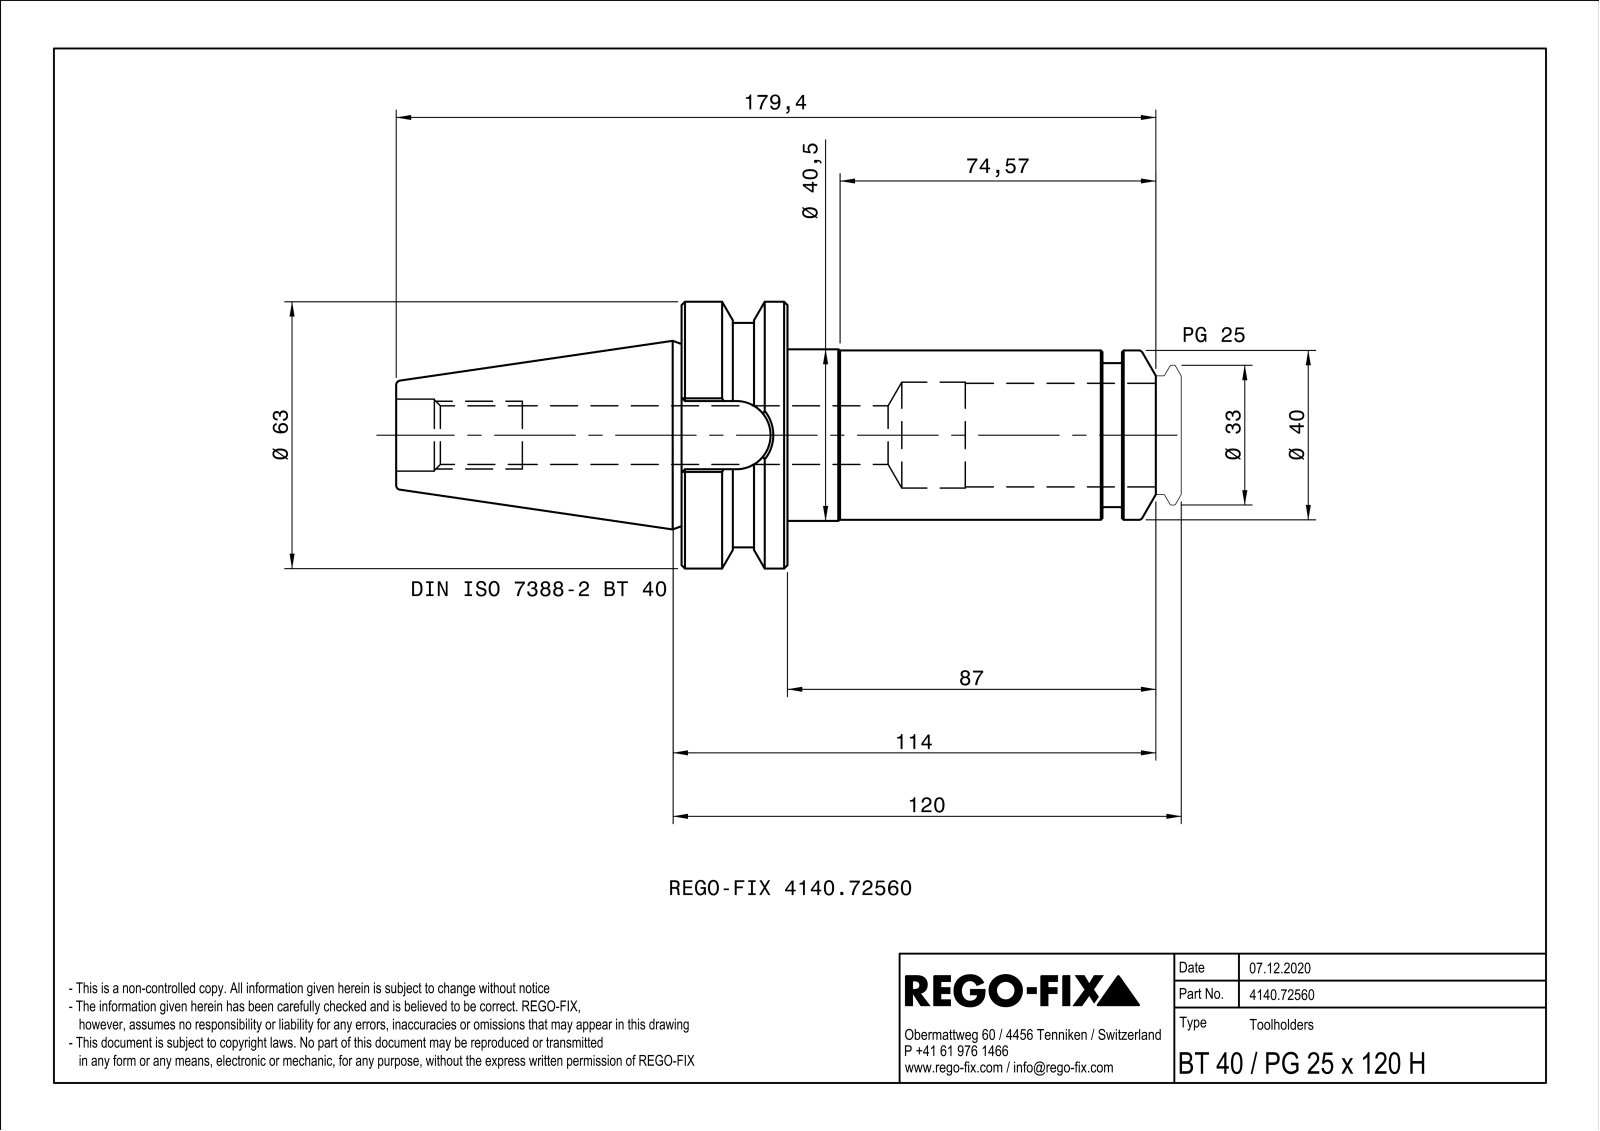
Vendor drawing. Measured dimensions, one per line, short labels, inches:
name: NOCUT
written by: SIEMENS PLM Software Solid Edge ST10 (AUTOMOTIVE_DESIGN)
unit: in
bodies: 1 solid, 100 faces (39 planar, 21 cylindrical, 40 other)
size: 7.063 × 2.48 × 2.48
volume: 11.79 in³; area: 60.78 in²
holes: 1× ⌀0.545, 1× ⌀0.669, 1× ⌀0.984
bosses: 1× ⌀2.48, 1× ⌀2.087, 1× ⌀1.594, 1× ⌀1.575, 1× ⌀1.339
rounds: 4× R0.02, 1× R0.317
face distances: 0.984, 1.776, 2.929, 3.913, 0.181, 3.11, 4.094, 6.748, 6.567, 3.638
